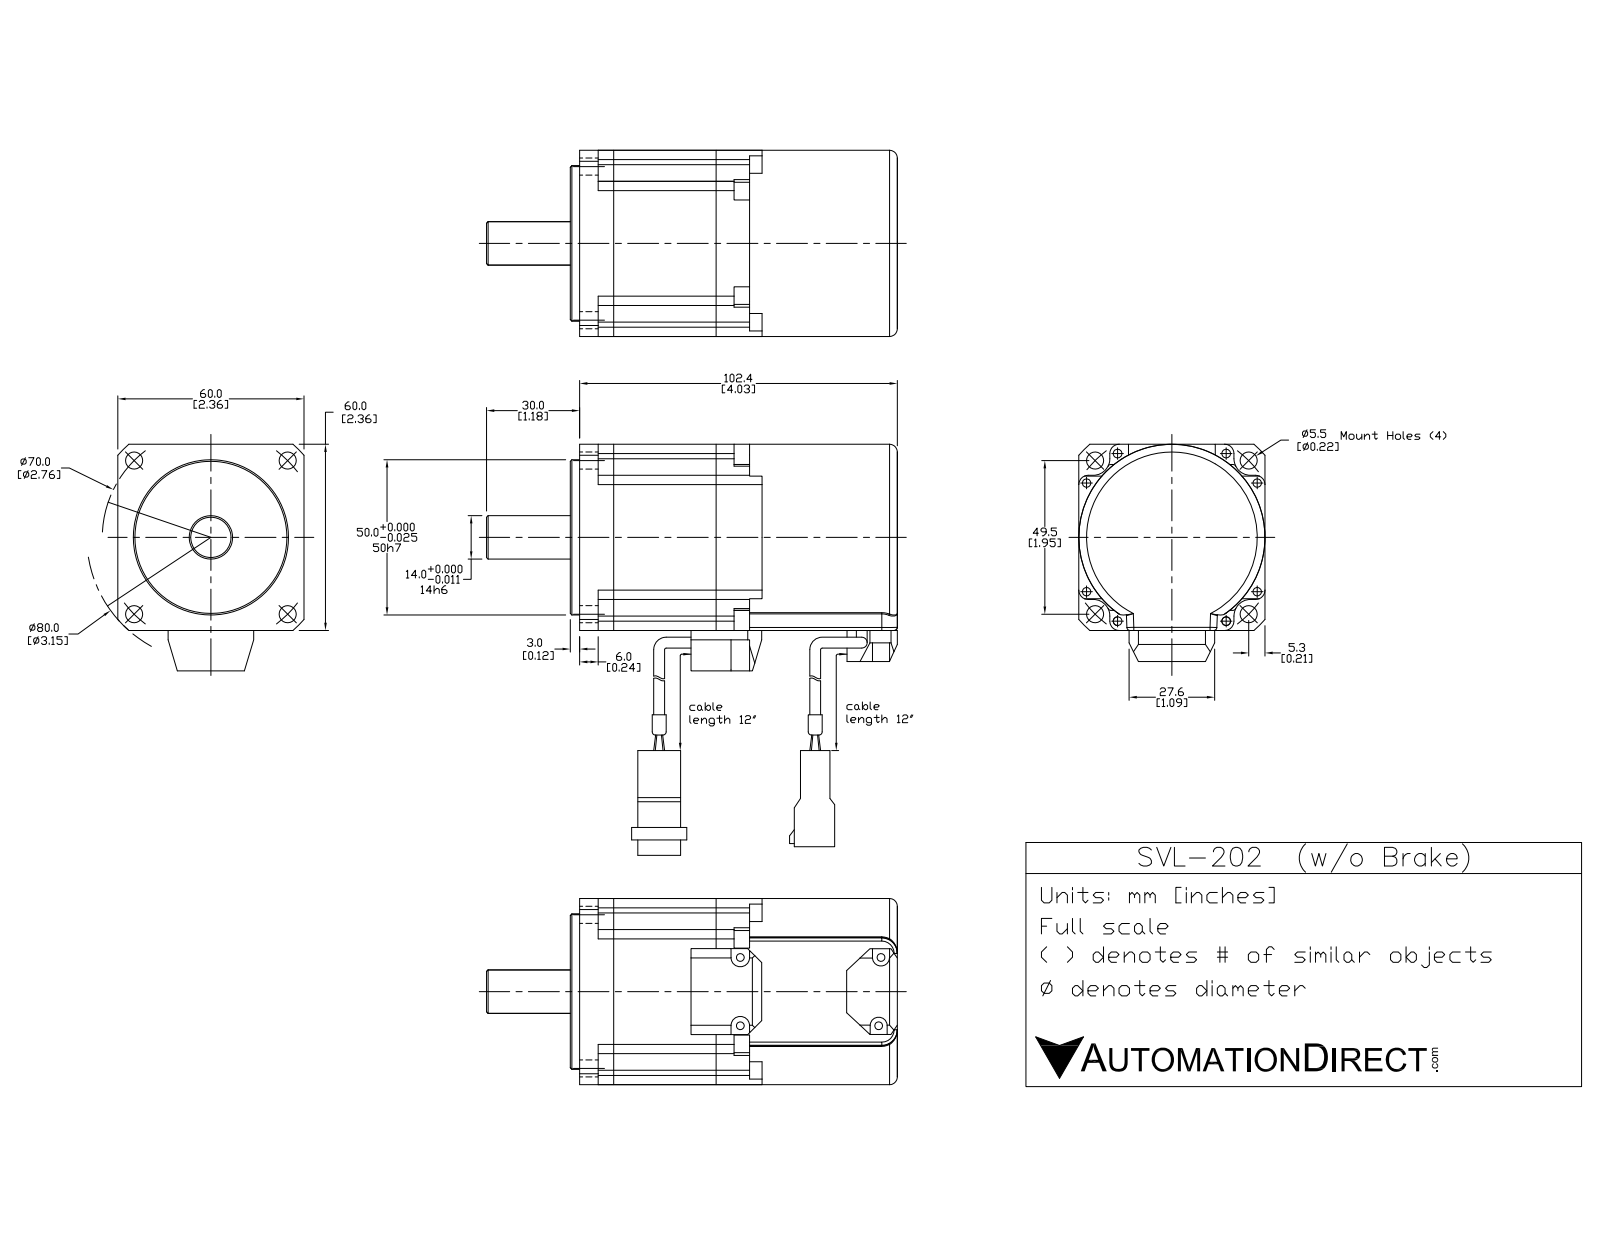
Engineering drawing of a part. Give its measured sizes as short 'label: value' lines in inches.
name: SVL-202
written by: SolidWorks 2015 (AUTOMOTIVE_DESIGN)
unit: in
bodies: 18 solids, 417 faces (241 planar, 141 cylindrical, 35 other)
size: 5.213 × 2.89 × 2.491
volume: 20.56 in³; area: 86.54 in²
holes: 4× ⌀0.217, 1× ⌀0.728
bosses: 5× ⌀0.217, 4× ⌀0.197, 4× ⌀0.138, 1× ⌀2.362, 1× ⌀1.969, 1× ⌀0.551, 1× ⌀0.276
rounds: 14× R0.039, 12× R0.118, 4× R0.079, 4× R0.098, 4× R0.108, 4× R0.209, 1× R1.575
face distances: 1.299, 0.449, 1.748, 1.85, 2.299, 2.362, 3.598, 1.732, 4.15, 0.551
hole spacings: 1.378, 1.949, 2.756
